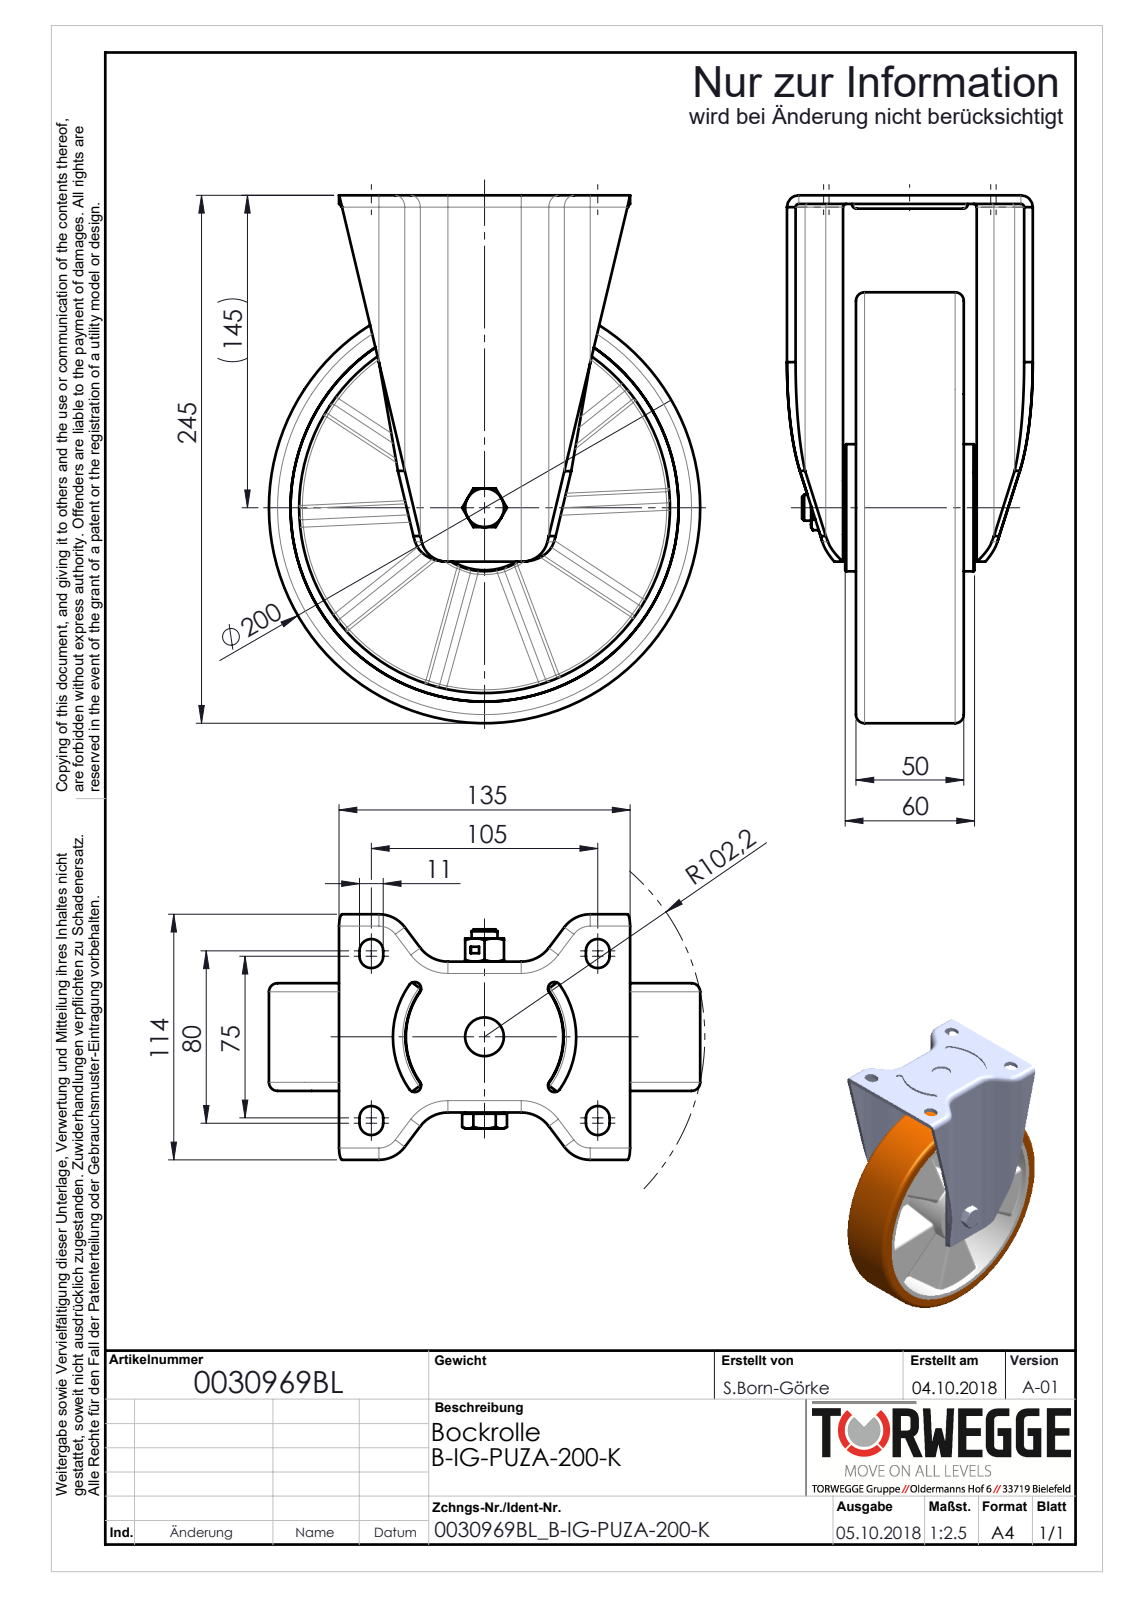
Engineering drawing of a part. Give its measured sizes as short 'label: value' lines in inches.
name: 0030969BL_B-IG-PUZA-200-K
written by: SolidWorks 2018 (AUTOMOTIVE_DESIGN)
unit: in
bodies: 0 solids, 594 faces (154 planar, 156 cylindrical, 284 other)
size: 9.646 × 7.874 × 4.488
holes: 1× ⌀0.402, 1× ⌀0.472, 1× ⌀0.48, 1× ⌀0.492, 1× ⌀0.709, 1× ⌀0.787, 1× ⌀0.807, 1× ⌀1.531, 1× ⌀1.85, 1× ⌀6.772, 1× ⌀7.087
bosses: 1× ⌀7.874, 1× ⌀2.323, 1× ⌀1.106, 1× ⌀0.984, 1× ⌀0.783, 1× ⌀0.709
rounds: 18× R0.059, 16× R0.138, 16× R0.217, 4× R0.087, 4× R0.118, 4× R0.433, 4× R0.591, 4× R0.63
face distances: 0.157, 0.236, 1.969, 0.09, 0.177, 1.319, 2.362, 0.413, 1.732, 1.555
